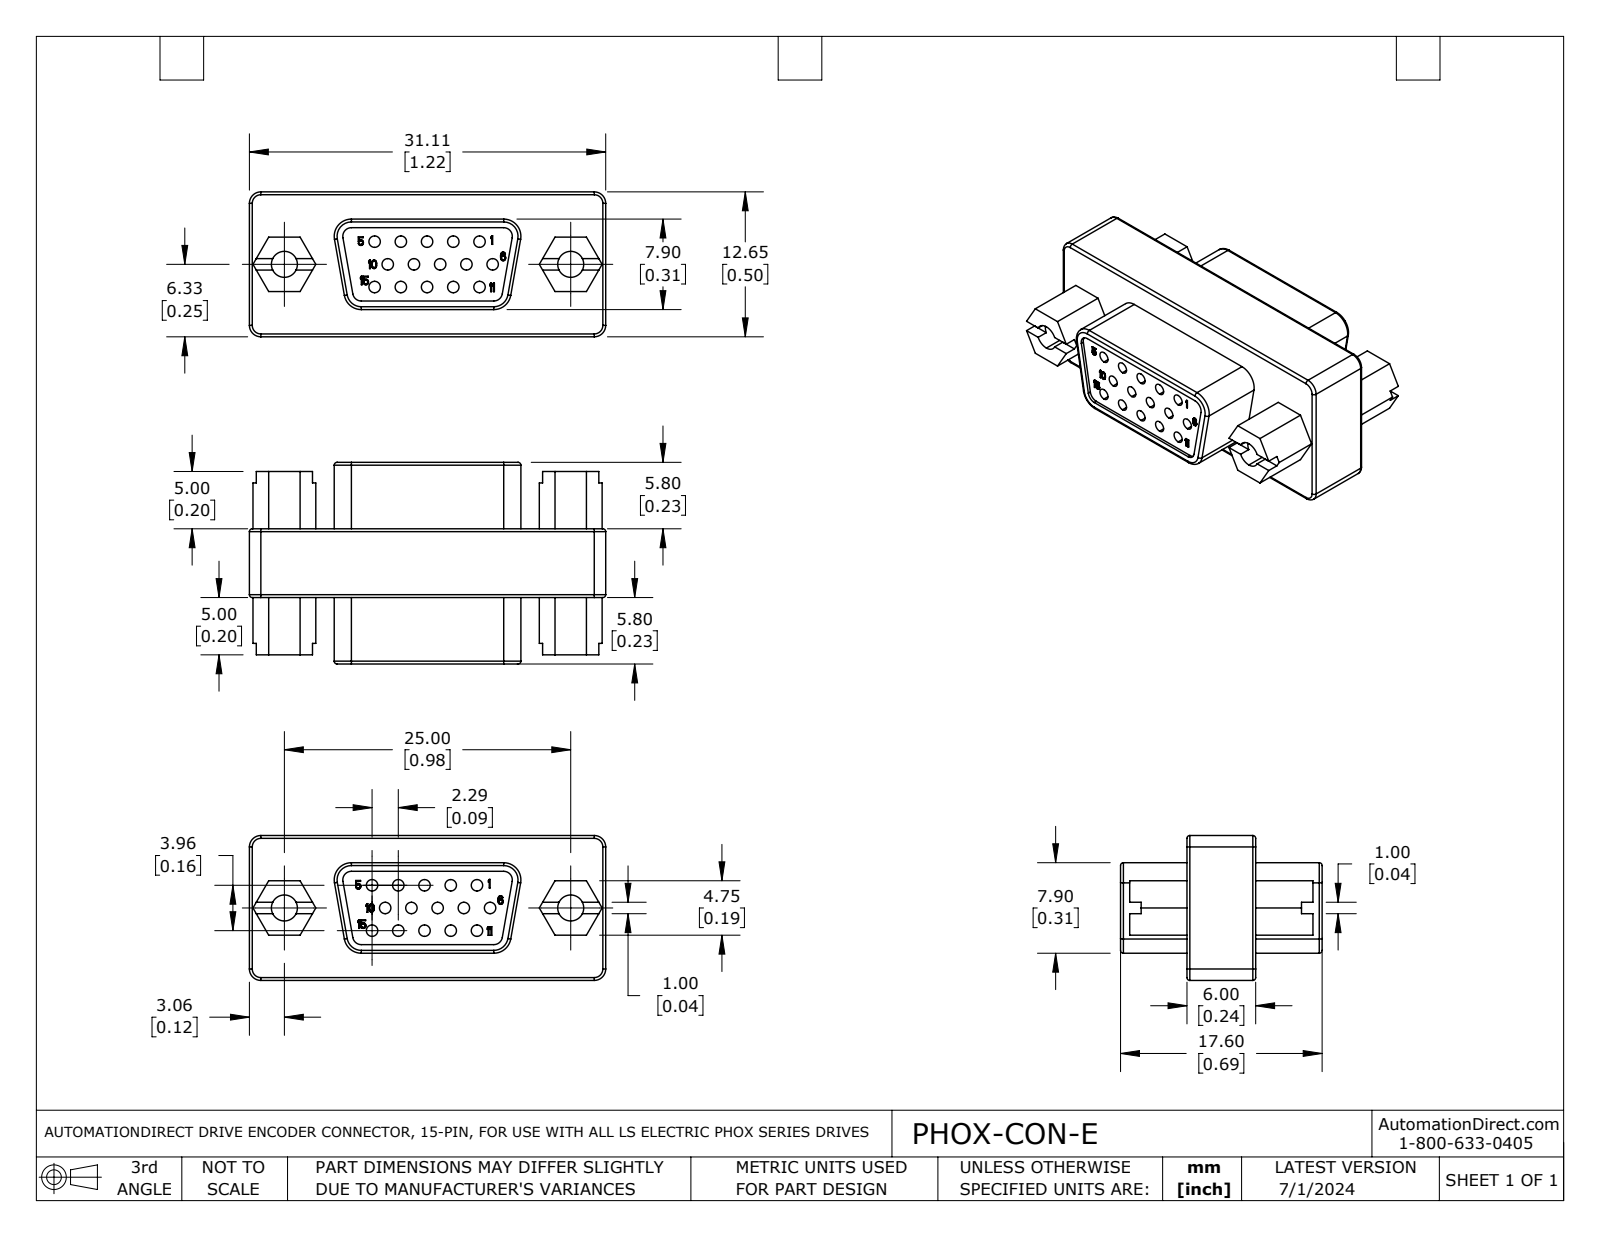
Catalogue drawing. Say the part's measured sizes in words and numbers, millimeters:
The part is named "PHOX-CON-E". Its 3-D file was written by "SolidWorks 2021 (AUTOMOTIVE_DESIGN)". It is 1 solid with 696 faces: 576 planar, 104 cylindrical and 16 other. Overall it measures 31.1 by 17.6 by 12.6 millimeters. Its volume is 3 870 cubic millimeters and its surface area 2 806 square millimeters. Round holes: 30 of diameter 1, 2 of diameter 2.3. Partial cylindrical surfaces (rounded edges, fillets, slot ends): 16 of radius 0.3, 4 of radius 0.8, 4 of radius 1, 4 of radius 1.5. The main face-to-face distances are 2.4, 10.3, 6, 12.6, 4.7, 11.6, 5.6, 7.9, 21.6, 17.1. The hole center spacings are 2.3, 4, 2.3, 4, 2.2, 4.6, 6, 3.7.
